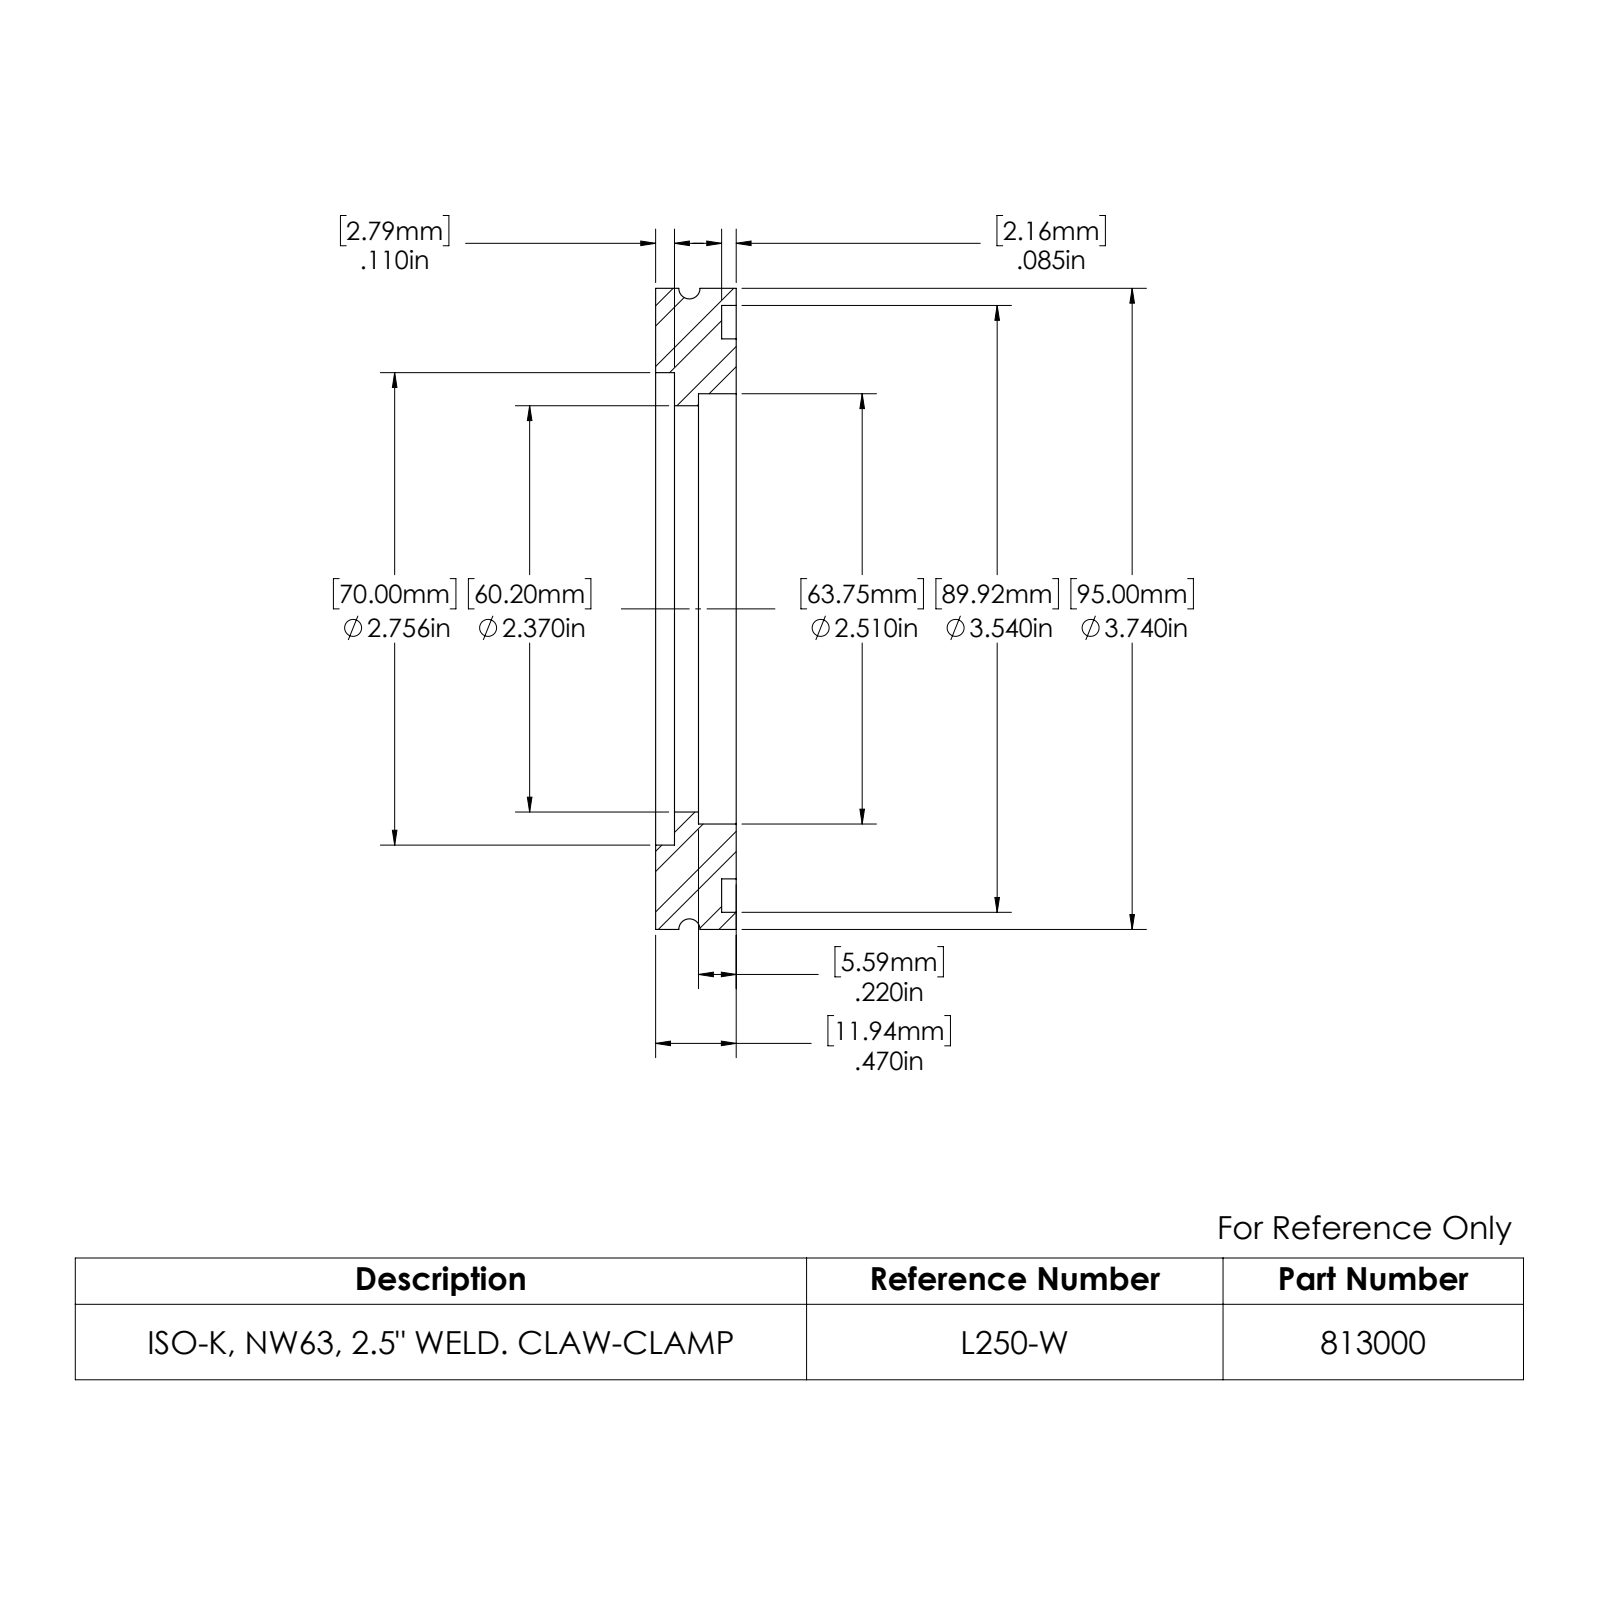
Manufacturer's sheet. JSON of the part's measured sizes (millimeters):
{"part_name": "813000", "step_written_by": "SolidWorks 2022 (AUTOMOTIVE_DESIGN)", "units": "millimeters", "bodies": {"solids": 1, "faces": 24, "planar": 6, "cylindrical": 14, "other": 4}, "overall_size": [95, 95, 11.9], "volume_mm3": 41900, "surface_area_mm2": 16110, "round_holes": [[60.2, 1], [63.8, 1], [70, 1], [89.9, 1]], "round_bosses_or_shafts": [[95, 1], [80, 1]], "face_to_face_distances": [11.9, 9.8, 2.2, 2.8, 7, 9.1, 6.4, 3.6, 3.4, 5.6]}
